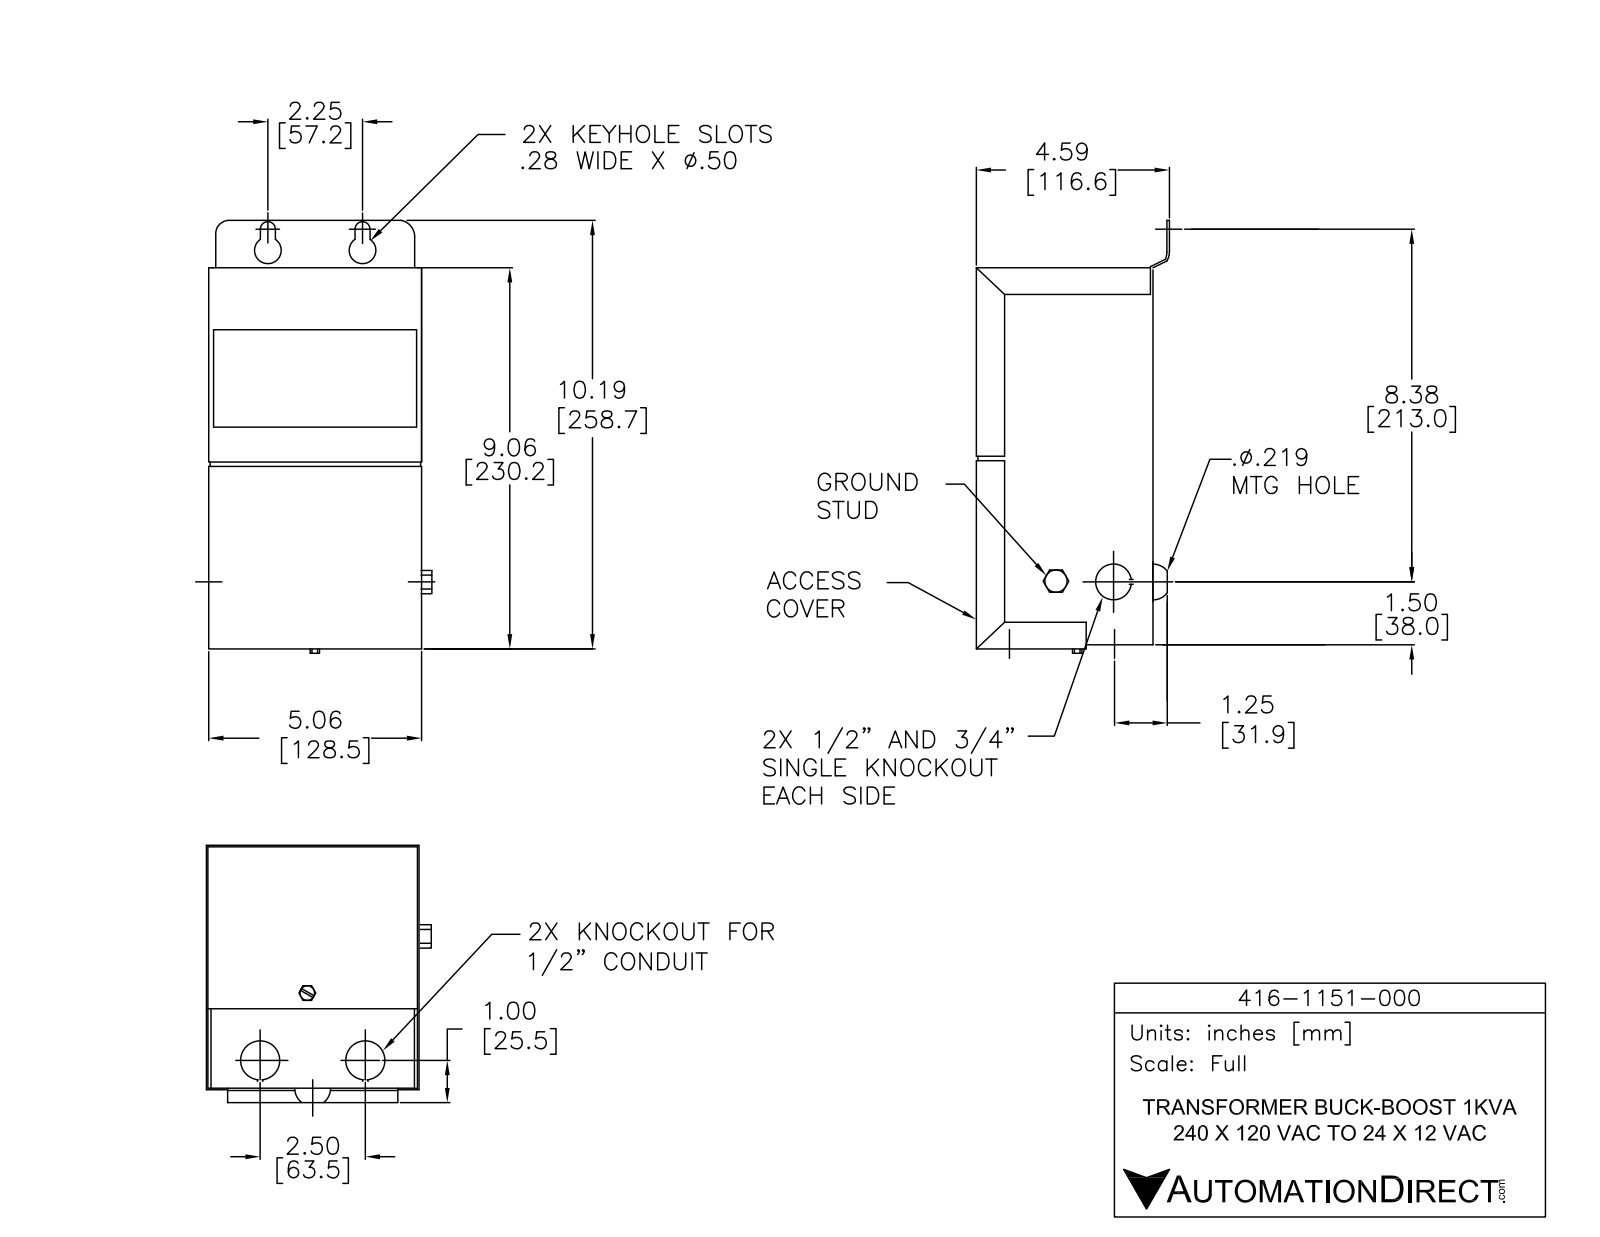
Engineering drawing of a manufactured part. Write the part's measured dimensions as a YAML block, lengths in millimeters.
part_name: "416-1151-000"
step_written_by: "SolidWorks 2013 (AUTOMOTIVE_DESIGN)"
units: millimeters
bodies: {solids: 1, faces: 159, planar: 91, cylindrical: 52, other: 16}
overall_size: [261.6, 131.3, 116.6]
volume: 3118000
surface_area: 145400
round_holes:
  - {diameter: 12.7, count: 2}
  - {diameter: 22.2, count: 2}
  - {diameter: 5.6, count: 1}
  - {diameter: 5.9, count: 1}
  - {diameter: 7.4, count: 1}
  - {diameter: 22.2, count: 1}
round_bosses_or_shafts:
  - {diameter: 28.6, count: 1}
partial_cylinders:
  - {radius: 1, count: 10}
  - {radius: 6.4, count: 10}
  - {radius: 3.6, count: 2}
  - {radius: 1.5, count: 1}
  - {radius: 3.8, count: 1}
  - {radius: 4.8, count: 1}
face_to_face_distances: [106.7, 126.5, 1, 127.5, 106.7, 230.1, 128.5, 229.1, 1, 9.9]
hole_center_spacings: [43.7, 207.5, 34.8, 57.2, 63.5]
